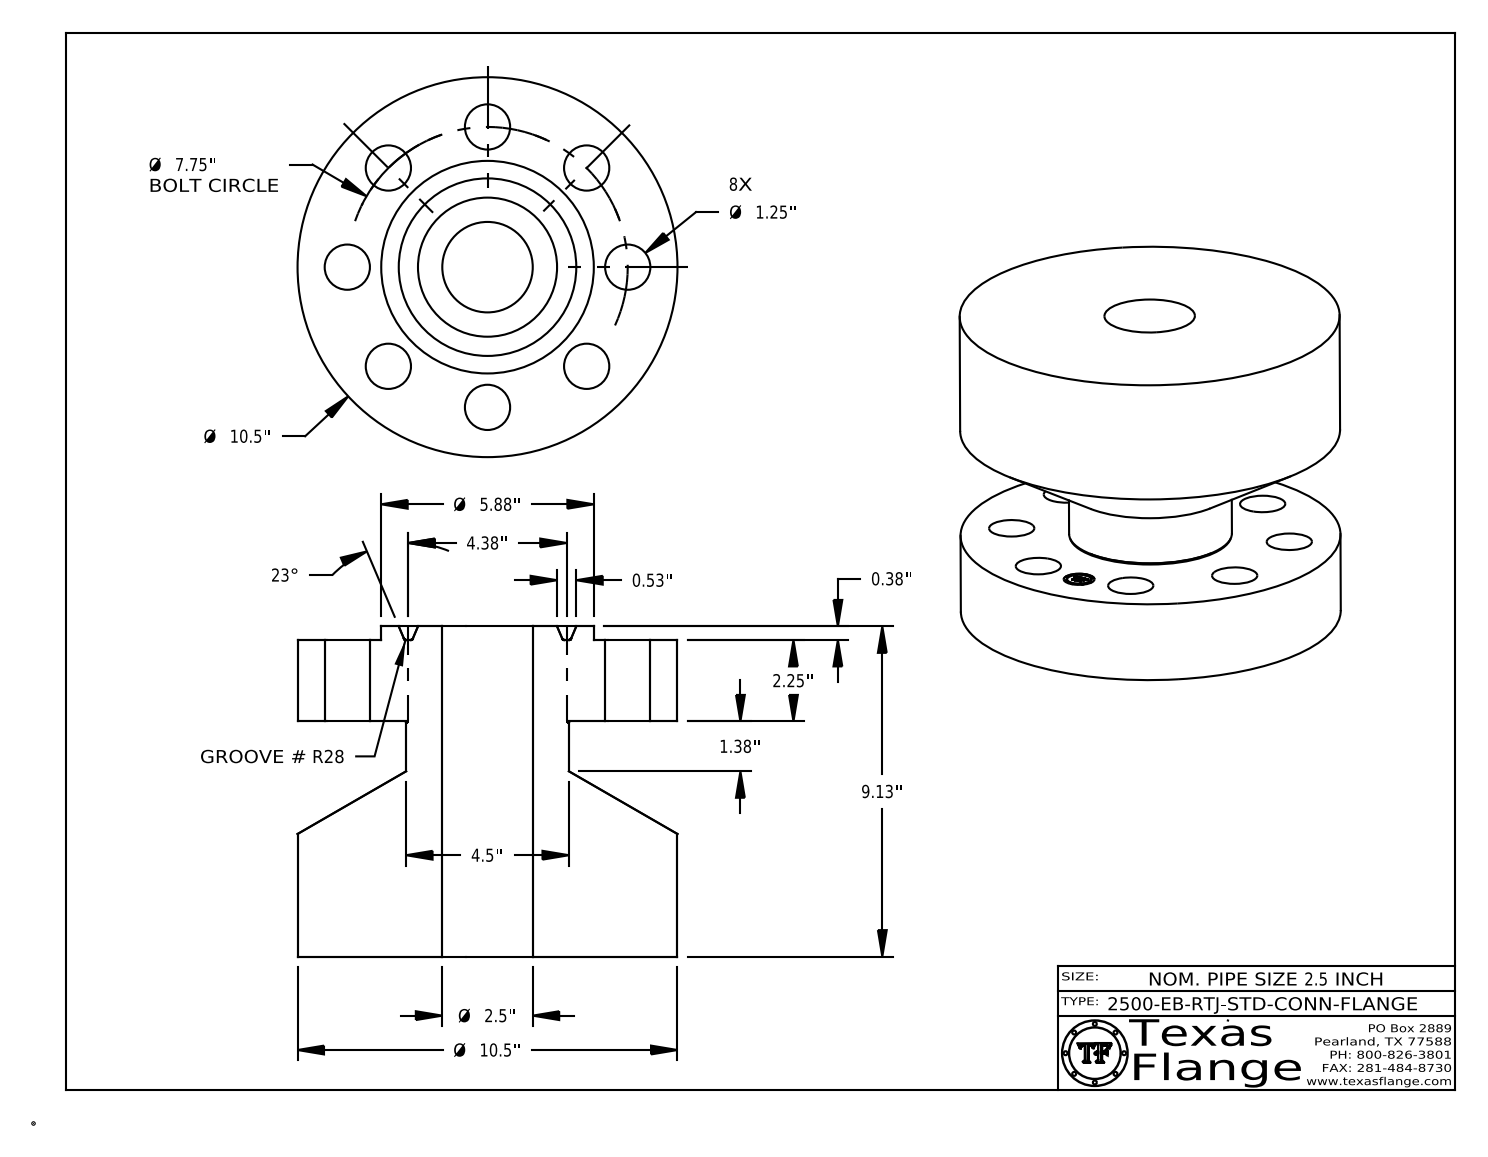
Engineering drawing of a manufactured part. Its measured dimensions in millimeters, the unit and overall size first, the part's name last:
Units: millimetres
Overall size (bounding box): 266.7 × 266.7 × 231.8
Round holes (diameter × count): ⌀31.8 ×8, ⌀21.6 ×1, ⌀63.5 ×1
Round bosses / shafts (diameter × count): ⌀1.3 ×8, ⌀266.7 ×1, ⌀149.2 ×1, ⌀114.3 ×1, ⌀17 ×1
Main face-to-face distances: 165.1, 57.2, 222.3, 9.5, 66.7, 231.8, 66.5, 57, 165.2, 6.5
Hole centre spacings: 75.3, 98.4, 139.2, 181.9, 196.9, 193.1, 38.4, 38.4
Volume: 8 720 000 mm³ · Surface area: 424 500 mm²
Bodies: 1 solid, 431 faces (371 planar, 46 cylindrical, 14 other)
Part name (STEP PRODUCT): 2.5-2500-EB-RTJ-STD-CONN-FLANGE
STEP written by: CATIA V5 STEP AP214 (AUTOMOTIVE_DESIGN)
